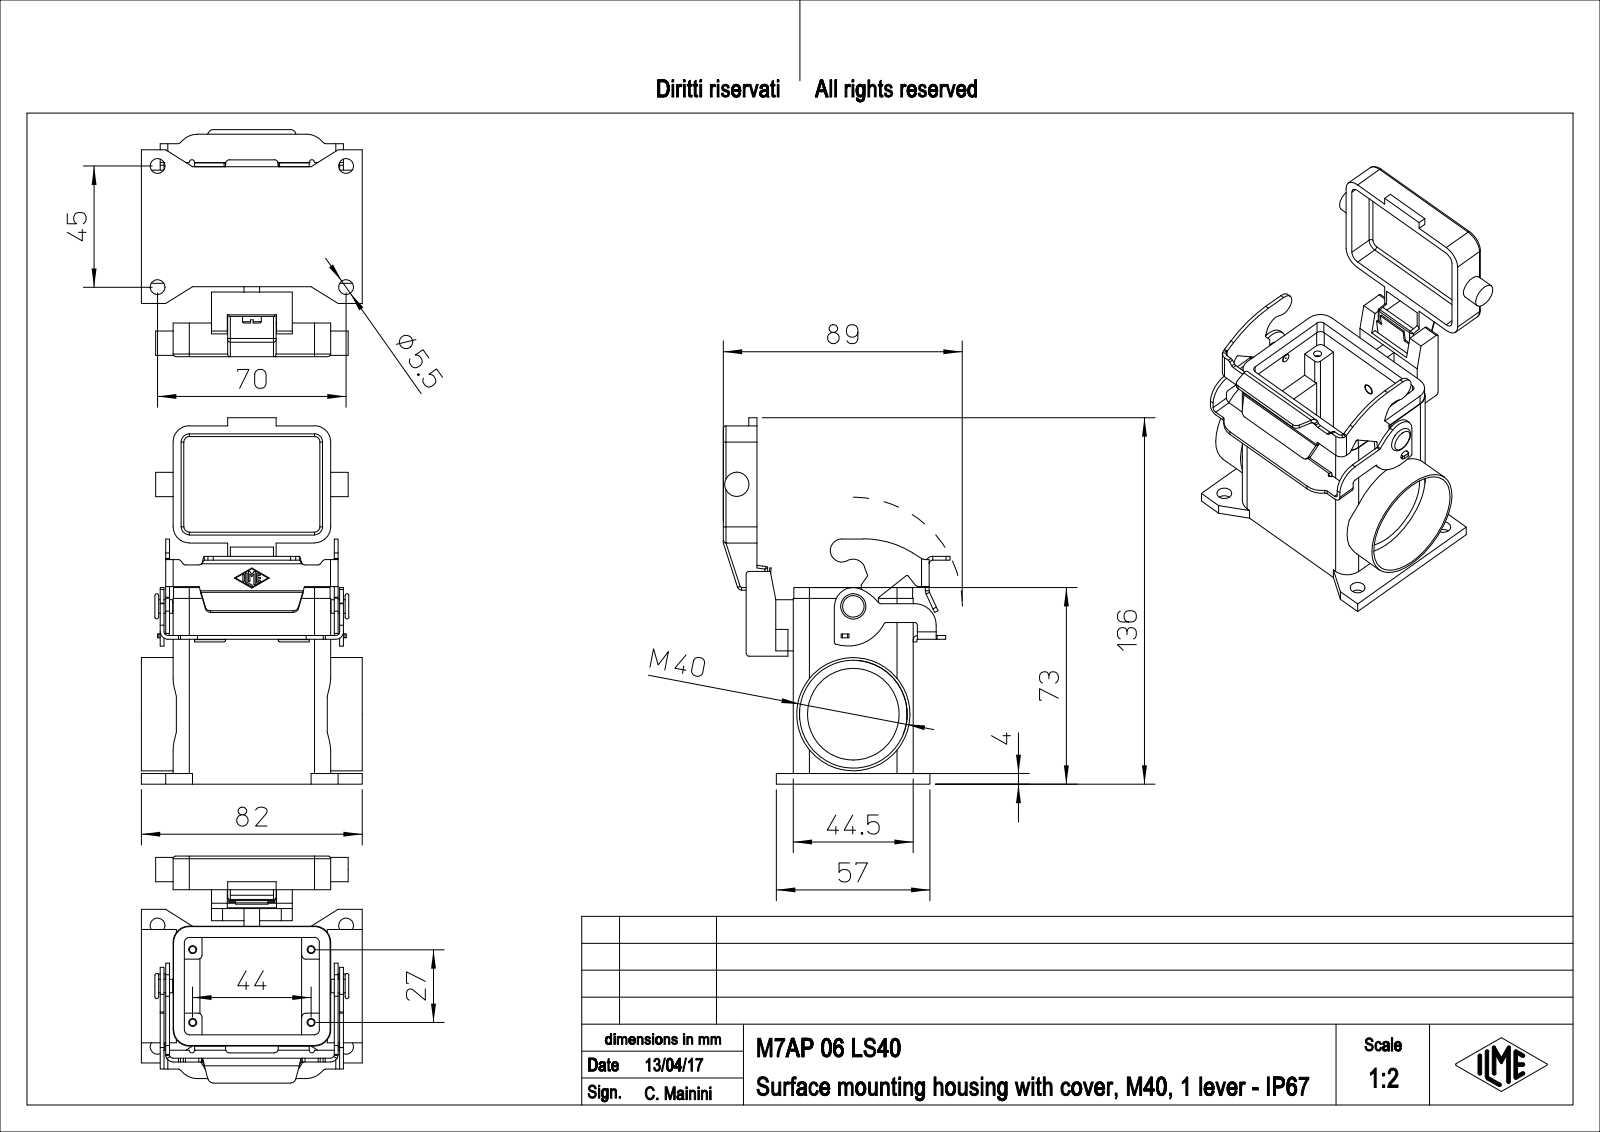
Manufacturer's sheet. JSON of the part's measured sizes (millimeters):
{"part_name": "M7AP_06_LS40", "step_written_by": "PTC Creo Elements/Direct Modeling 19.0E 27-Jun-2016 (C) Parametric Technology GmbH (AUTOMOTIVE_DESIGN)", "units": "millimeters", "bodies": {"solids": 1, "faces": 548, "planar": 285, "cylindrical": 223, "other": 40}, "overall_size": [136, 84.23, 82], "volume_mm3": 102812, "surface_area_mm2": 65260, "round_holes": [[2.46, 4], [3, 4], [5.5, 4], [3.5, 1], [4, 1], [34, 1], [40, 1]], "round_bosses_or_shafts": [[42, 1], [9, 1], [7, 1], [5, 1], [4, 1], [3.2, 1], [3, 1]], "partial_cylinders_radius": [[1, 31], [0.25, 16], [0.5, 13], [1.5, 12], [2, 8], [6, 8], [1.4, 6], [2.8, 6]], "face_to_face_distances": [4, 40.5, 1.4, 44.5, 2.5, 36.5, 64, 68, 70.5, 66.5], "hole_center_spacings": [15.81, 38.28, 57.71, 67.42, 27, 44, 45, 51.62]}
